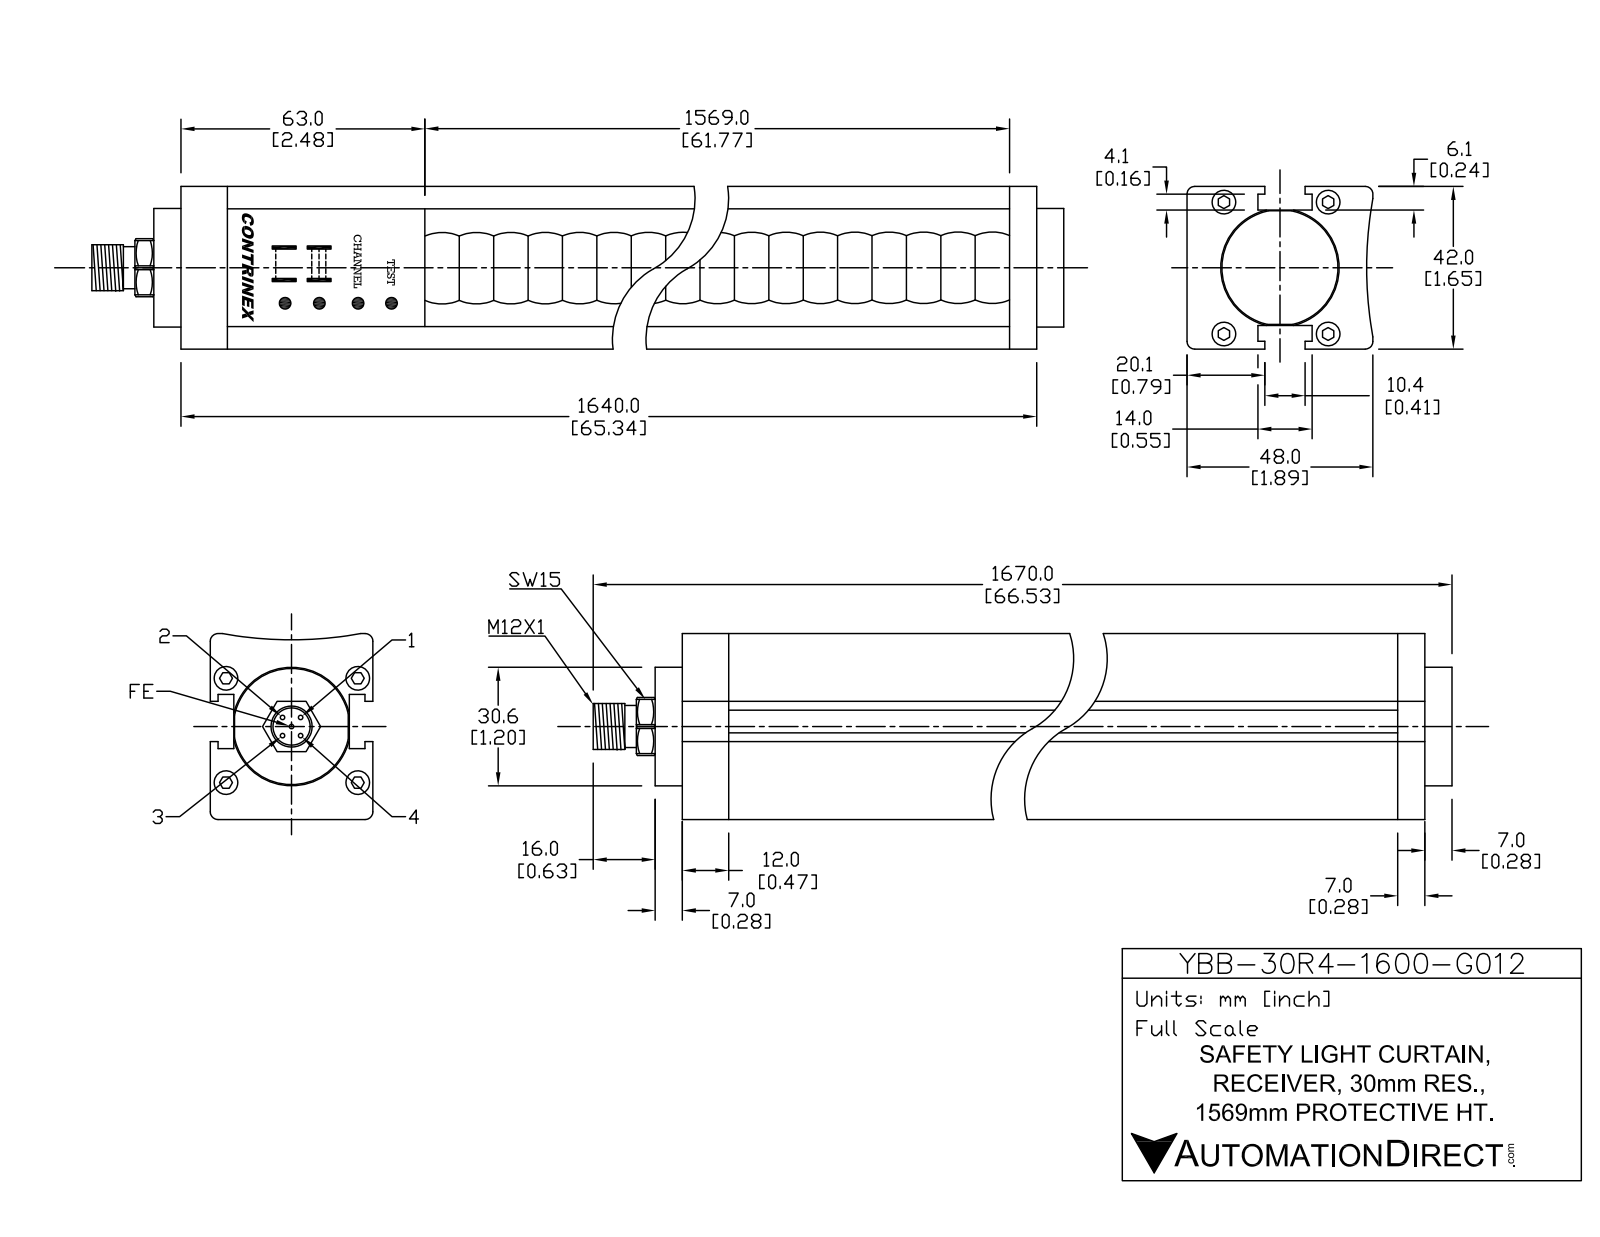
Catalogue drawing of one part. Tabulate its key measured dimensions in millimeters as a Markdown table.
| quantity | value |
| --- | --- |
| part name | YBB-30R4-1600-G012 |
| STEP written by | SolidWorks 2016 (AUTOMOTIVE_DESIGN) |
| units | millimeters |
| bodies | 19 solids, 440 faces (208 planar, 168 cylindrical, 64 other) |
| overall size | 1670 × 48 × 42 |
| volume | 2 946 000 mm³ |
| surface area | 367 270 mm² |
| round holes (diameter × count) | 6 × 4, 8.5 × 1, 32 × 1 |
| round bosses / shafts (diameter × count) | 1 × 5, 5.5 × 4, 30.6 × 1, 12 × 1, 10.5 × 1 |
| partial cylindrical surfaces (radius × count) | 1 × 48, 0.5 × 4, 0.55 × 2, 8.2 × 1, 100 × 1 |
| main face-to-face distances | 6.3, 35.7, 42, 29.4, 14, 17.2, 31.2, 15.7, 29.7, 46.9 |
| hole center spacings | 21.04, 22.34, 26.9, 34, 43.35 |
